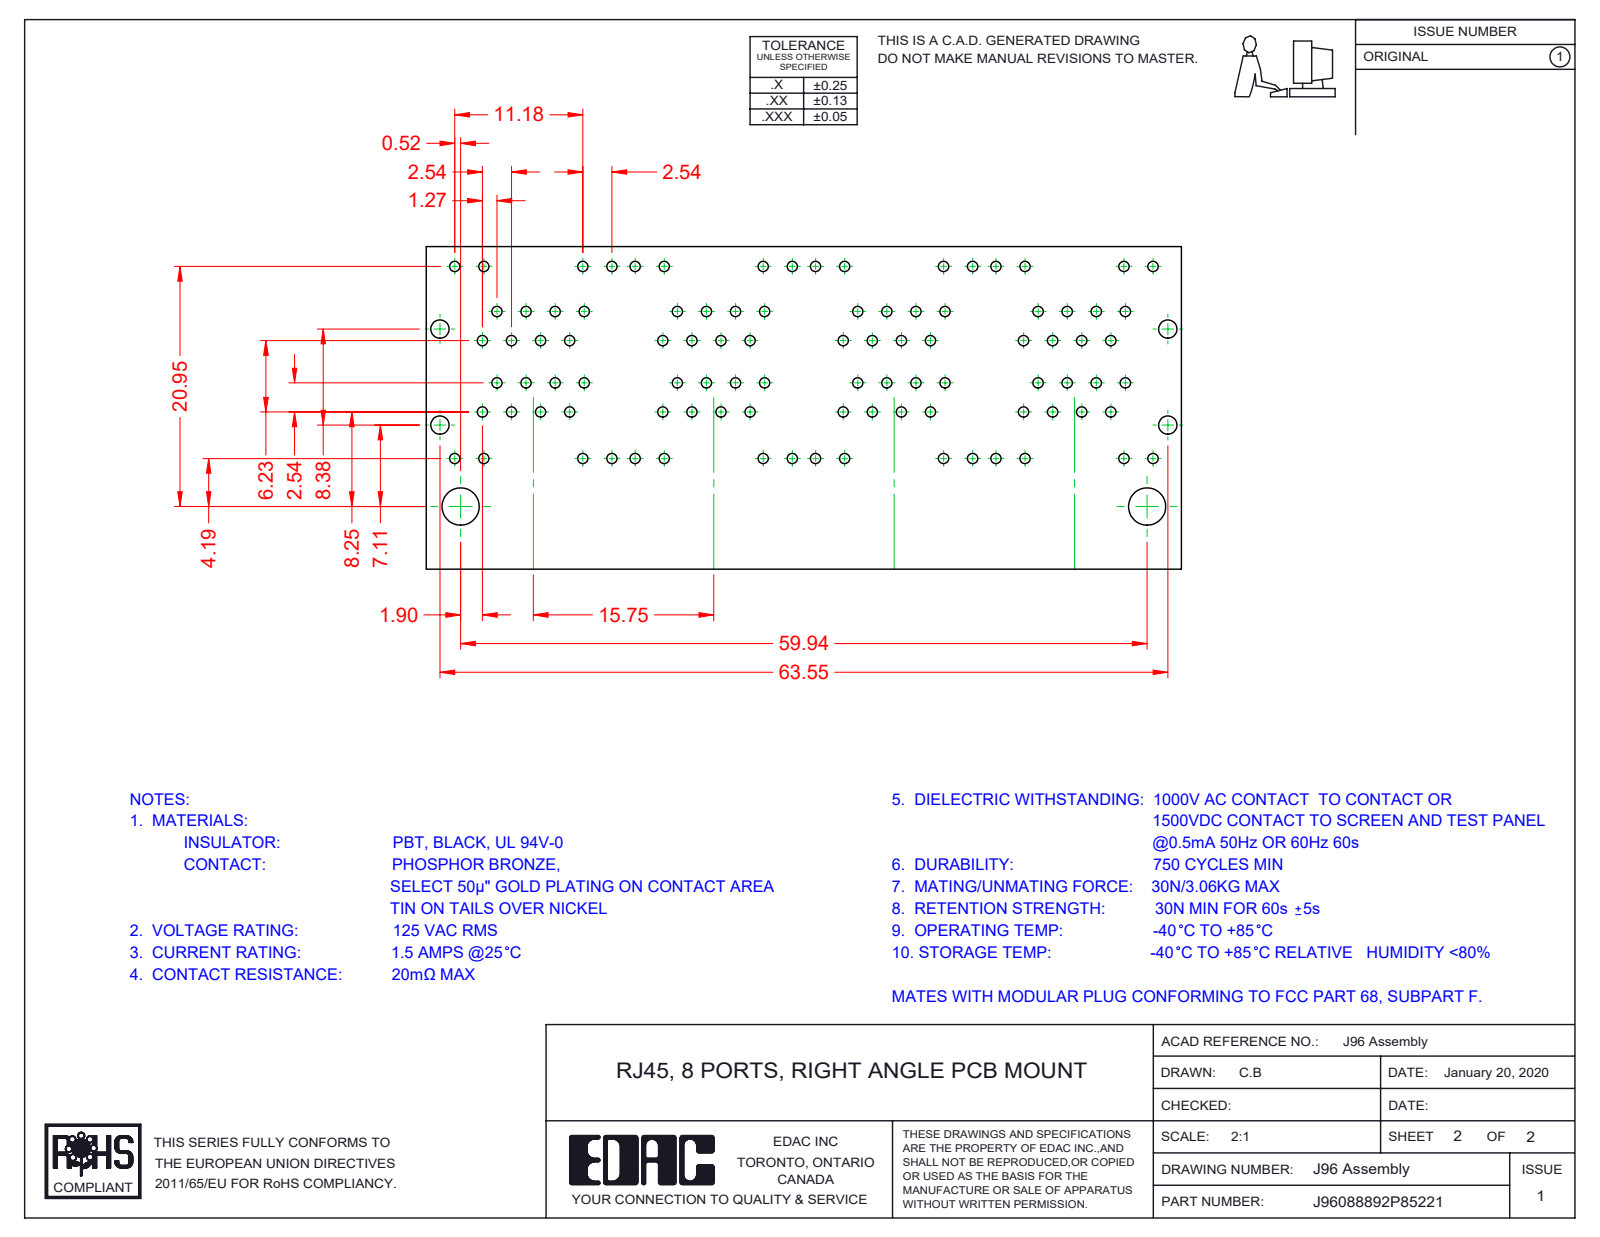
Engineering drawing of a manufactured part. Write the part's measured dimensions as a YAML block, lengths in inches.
part_name: "96 LED LH Lower_8-Red-Yellow; 96 Contact Lock Upper; 96 Insulator_8 Ports; 96 LED RH Upper_5-Green-Yellow (+8 more)"
step_written_by: "SolidWorks 2016 (CONFIG_CONTROL_DESIGN)"
units: inches
bodies: {solids: 96, faces: 7836, planar: 6105, cylindrical: 1420, other: 311}
overall_size: [2.652, 1.235, 1.129]
volume: 1.474
surface_area: 98.57
round_holes:
  - {diameter: 0.067, count: 3}
round_bosses_or_shafts:
  - {diameter: 0.066, count: 3}
partial_cylinders:
  - {radius: 0.01, count: 124}
  - {radius: 0.014, count: 73}
  - {radius: 0.039, count: 72}
  - {radius: 0.02, count: 49}
  - {radius: 0.036, count: 32}
  - {radius: 0.008, count: 27}
  - {radius: 0.011, count: 14}
  - {radius: 0.028, count: 11}
face_to_face_distances: [0.62, 0.014, 0.392, 0.046, 0.063, 0.021, 0.393, 0.401, 0.499, 0.133]
hole_center_spacings: [0.62, 1.24]
